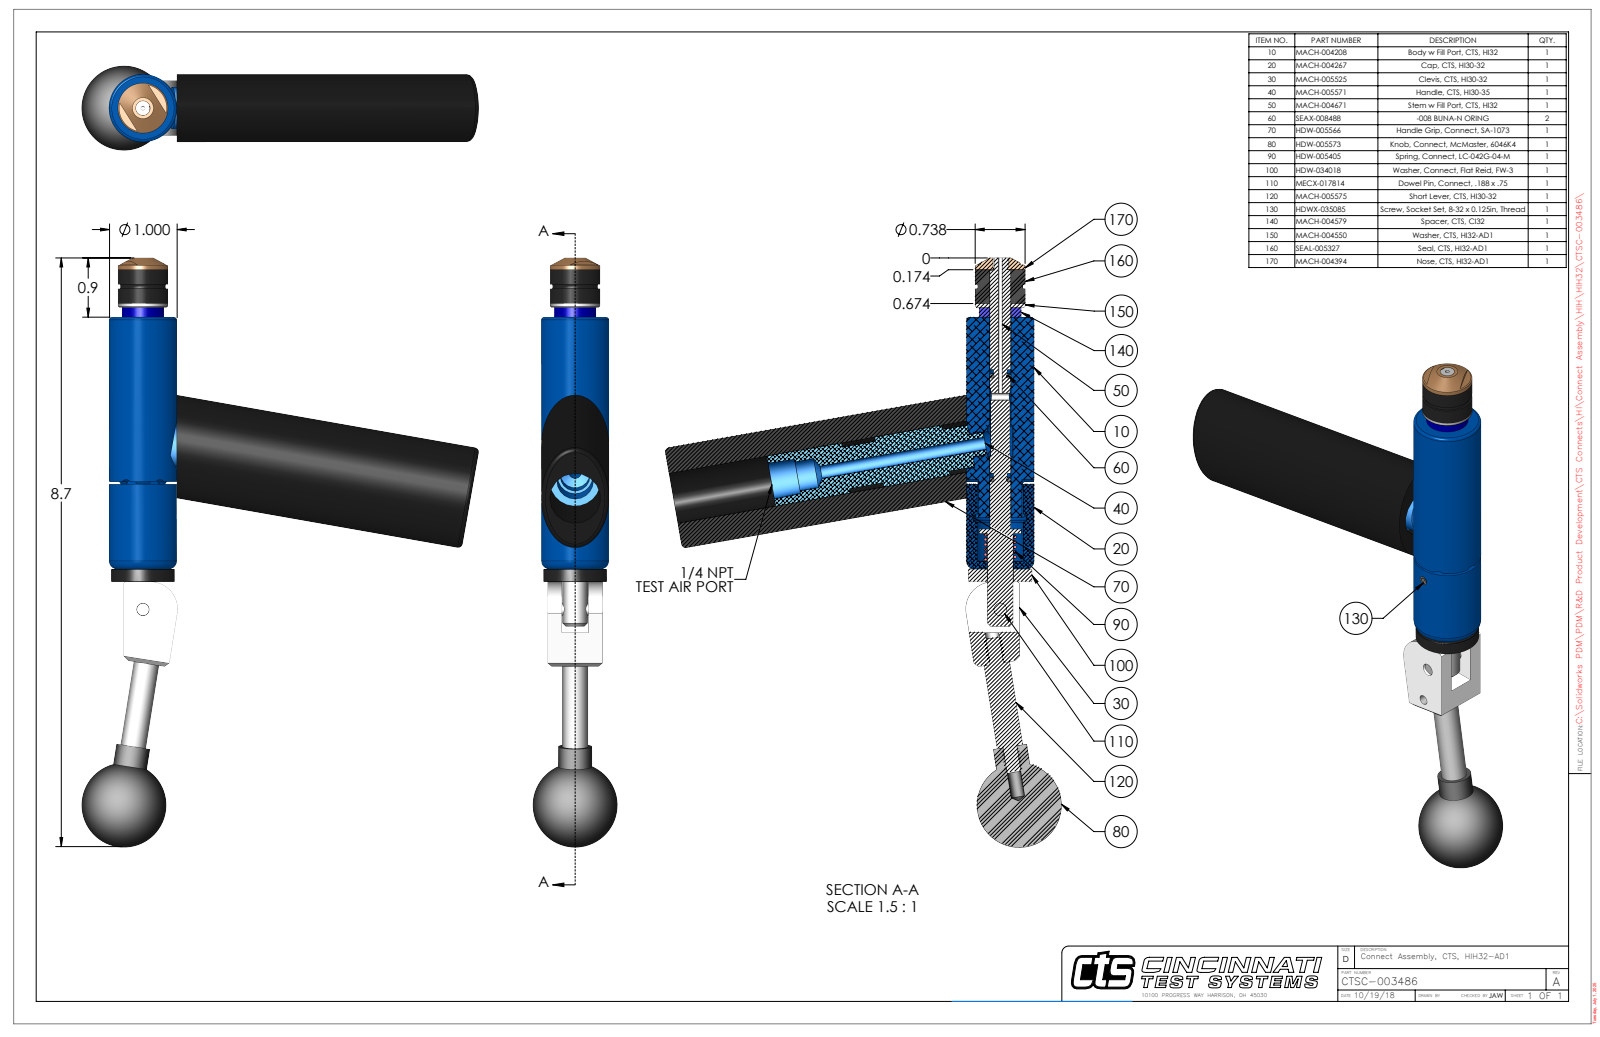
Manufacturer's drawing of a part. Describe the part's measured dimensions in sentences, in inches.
The part is named "CTSC-003486". Its 3-D file was written by "SolidWorks 2023 (AUTOMOTIVE_DESIGN)". It is 11 solids with 321 faces: 119 planar, 130 cylindrical and 72 other. Overall it measures 8.704 by 5.856 by 1.25 inches. Its volume is 9.379 cubic inches and its surface area 78.22 square inches. Round holes: 2 of diameter 0.201, 1 of diameter 0.063, 1 of diameter 0.109, 1 of diameter 0.113, 1 of diameter 0.136, 1 of diameter 0.15, 1 of diameter 0.187, 1 of diameter 0.189, 1 of diameter 0.213, 1 of diameter 0.31, 1 of diameter 0.314, 1 of diameter 0.316. Round bosses or shafts: 2 of diameter 0.25, 2 of diameter 0.201, 1 of diameter 1, 1 of diameter 0.936, 1 of diameter 0.75, 1 of diameter 0.738, 1 of diameter 0.62, 1 of diameter 0.618. Partial cylindrical surfaces (rounded edges, fillets, slot ends): 6 of radius 0.093, 2 of radius 0.029, 1 of radius 0.166, 1 of radius 0.325, 1 of radius 0.4, 1 of radius 0.442, 1 of radius 0.443. The main face-to-face distances are 0.21, 0.602, 3.719, 0.812, 0.702, 4.42, 0.5, 4.608, 3.906, 0.187. The hole center spacings are 0.599, 1.658, 2.252.
